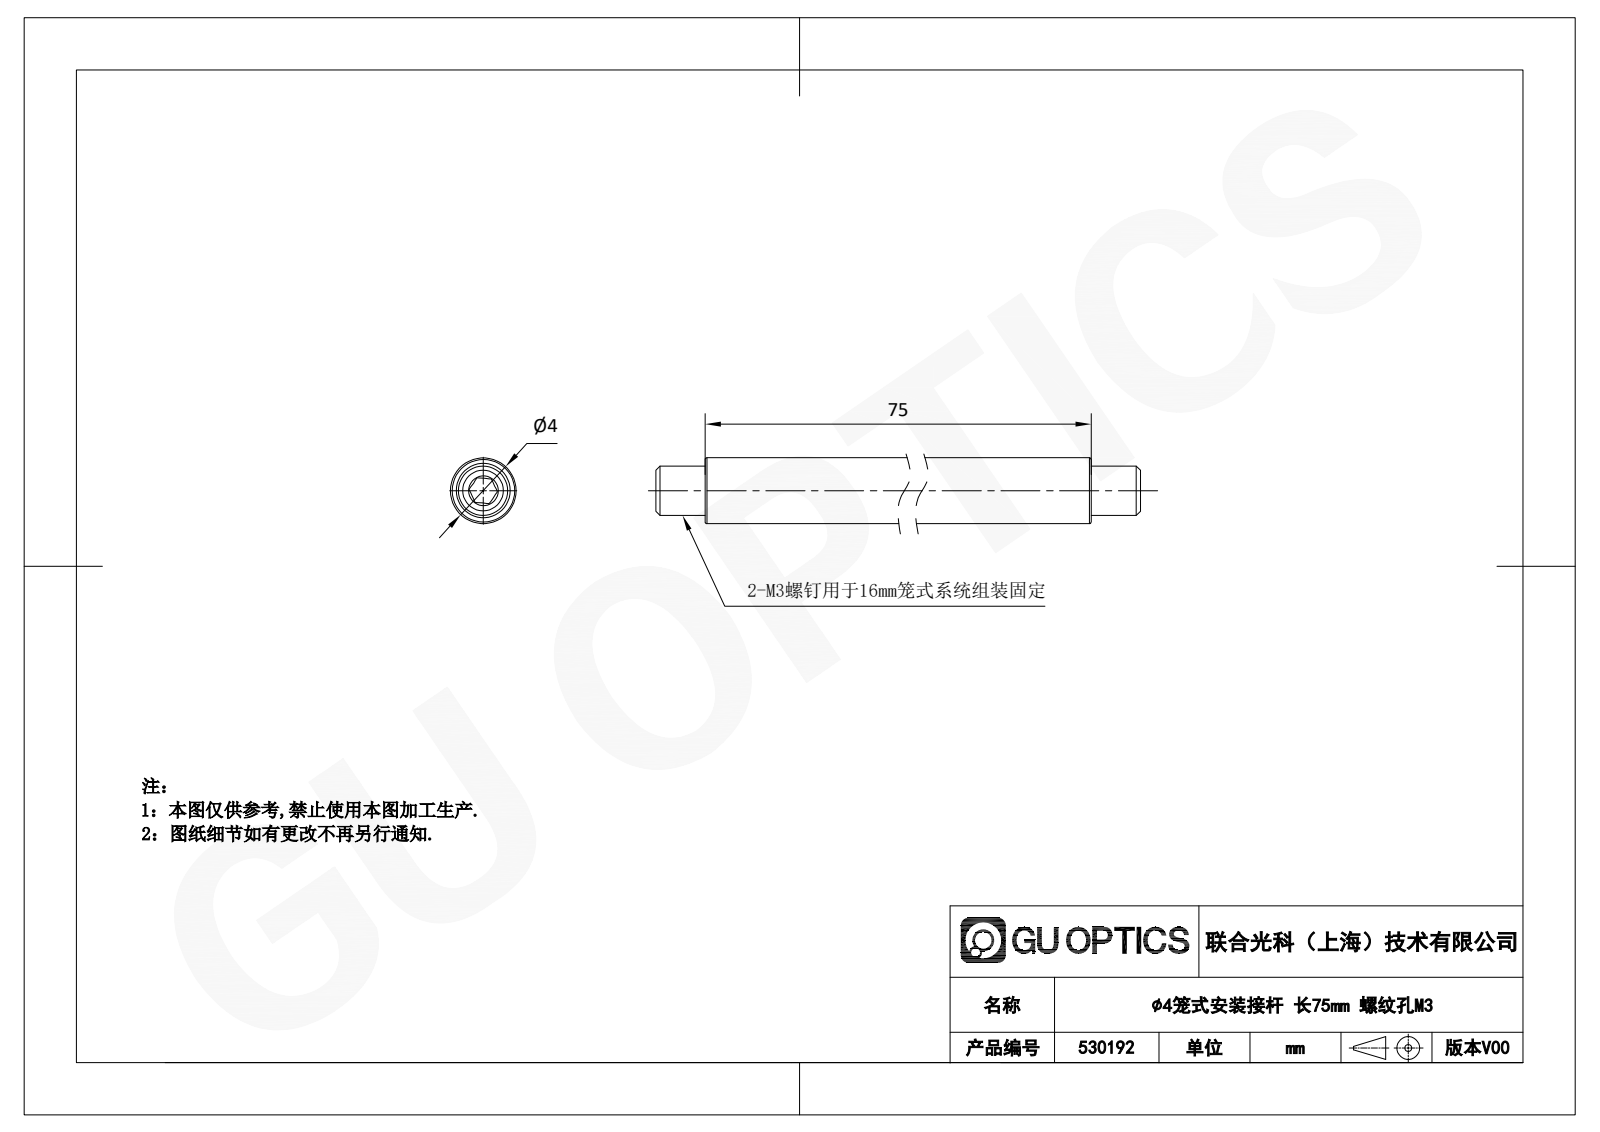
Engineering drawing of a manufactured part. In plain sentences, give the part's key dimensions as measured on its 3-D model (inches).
The part is named "530192". Its 3-D file was written by "SolidWorks 2020 (CONFIG_CONTROL_DESIGN)". It is 3 solids with 37 faces: 20 planar, 5 cylindrical and 12 other. Overall it measures 3.346 by 0.157 by 0.157 inches. Its volume is 0.061 cubic inches and its surface area 1.91 square inches. Round holes: 1 of diameter 0.098. Round bosses or shafts: 1 of diameter 0.157, 1 of diameter 0.118. The main face-to-face distances are 0.118, 2.835, 0.197, 0.315, 3.031, 3.15, 0.059, 2.953, 0.039, 3.307.
